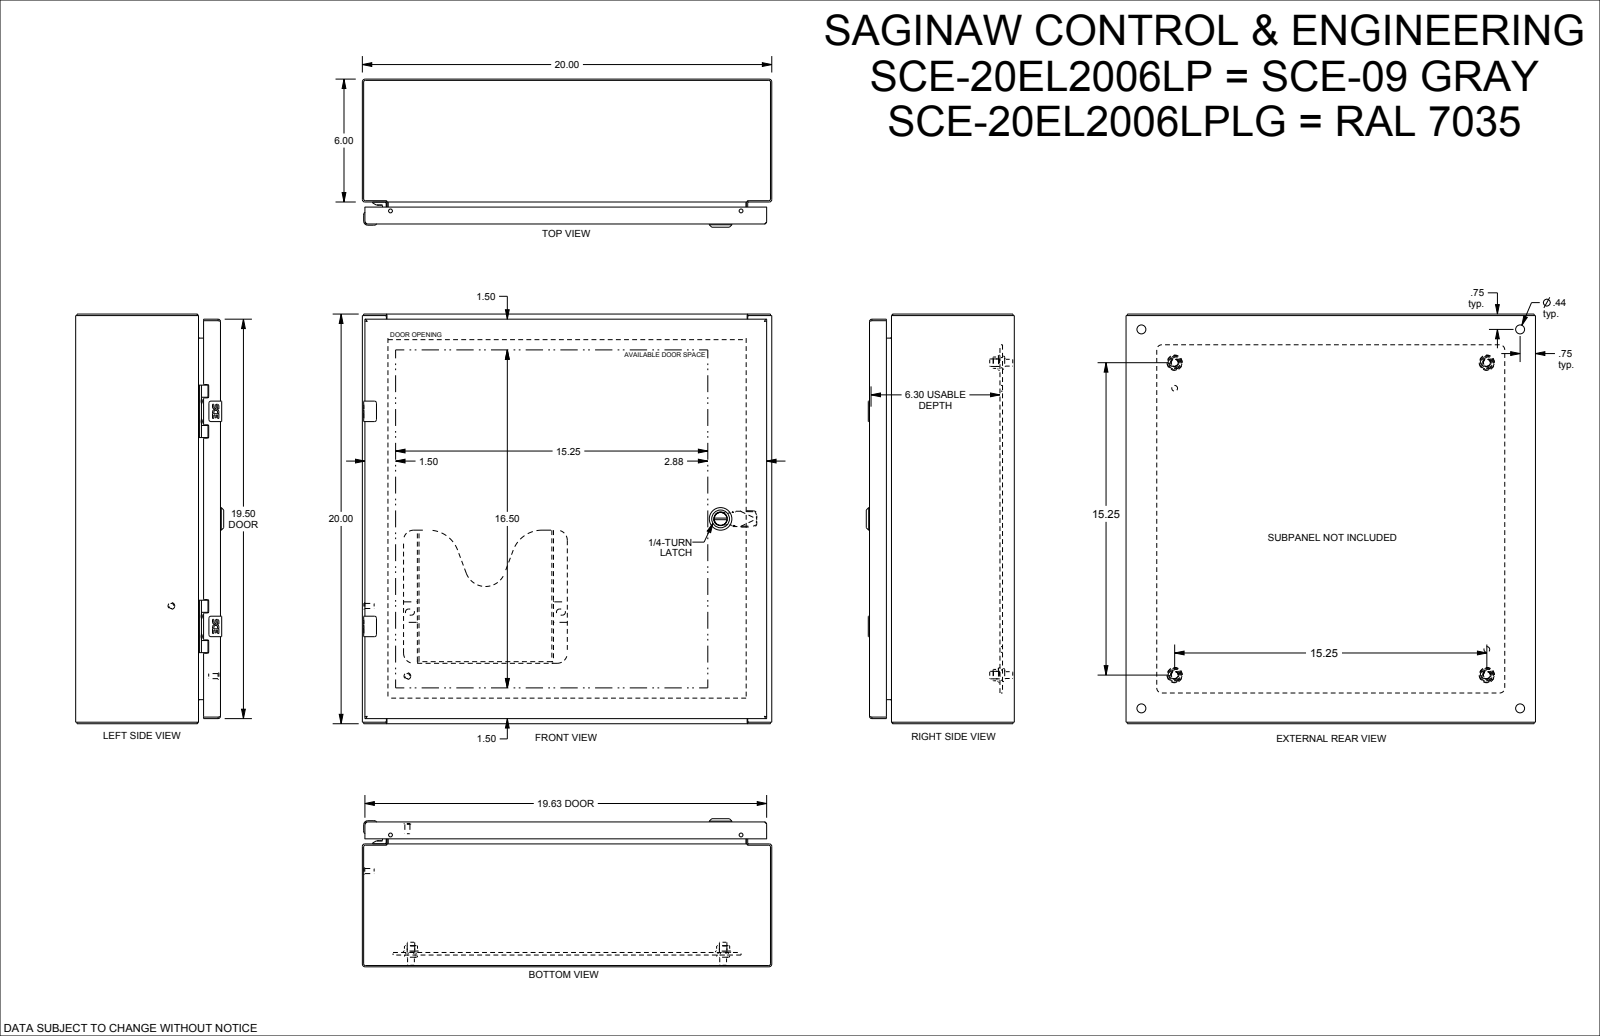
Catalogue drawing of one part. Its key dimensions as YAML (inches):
part_name: "SCE-20EL2006LP"
step_written_by: "SolidWorks 2021 (AUTOMOTIVE_DESIGN)"
units: inches
bodies: {solids: 43, faces: 2548, planar: 940, cylindrical: 754, other: 854}
overall_size: [20, 20, 7.23]
volume: 157.7
surface_area: 3812
round_holes:
  - {diameter: 0.172, count: 4}
  - {diameter: 0.205, count: 4}
  - {diameter: 0.244, count: 4}
  - {diameter: 0.266, count: 4}
  - {diameter: 0.367, count: 4}
  - {diameter: 0.375, count: 4}
  - {diameter: 0.437, count: 4}
  - {diameter: 0.5, count: 4}
  - {diameter: 0.04, count: 2}
  - {diameter: 0.188, count: 2}
  - {diameter: 0.218, count: 2}
  - {diameter: 0.25, count: 2}
round_bosses_or_shafts:
  - {diameter: 0.17, count: 6}
  - {diameter: 0.366, count: 4}
  - {diameter: 0.332, count: 4}
  - {diameter: 0.25, count: 4}
  - {diameter: 0.248, count: 4}
  - {diameter: 0.24, count: 4}
  - {diameter: 0.196, count: 3}
  - {diameter: 0.563, count: 2}
partial_cylinders:
  - {radius: 0.012, count: 30}
  - {radius: 0.01, count: 28}
  - {radius: 0.015, count: 24}
  - {radius: 0.04, count: 17}
  - {radius: 0.06, count: 13}
  - {radius: 0.02, count: 12}
  - {radius: 0.025, count: 12}
  - {radius: 0.029, count: 12}
face_to_face_distances: [0.075, 19.925, 0.06, 7.073, 6.998, 7.013, 6.938, 0.125, 0.625, 0.7]
hole_center_spacings: [16.953, 0.985, 10.5, 0.02, 0.493, 0.494, 2.298, 4.493]
